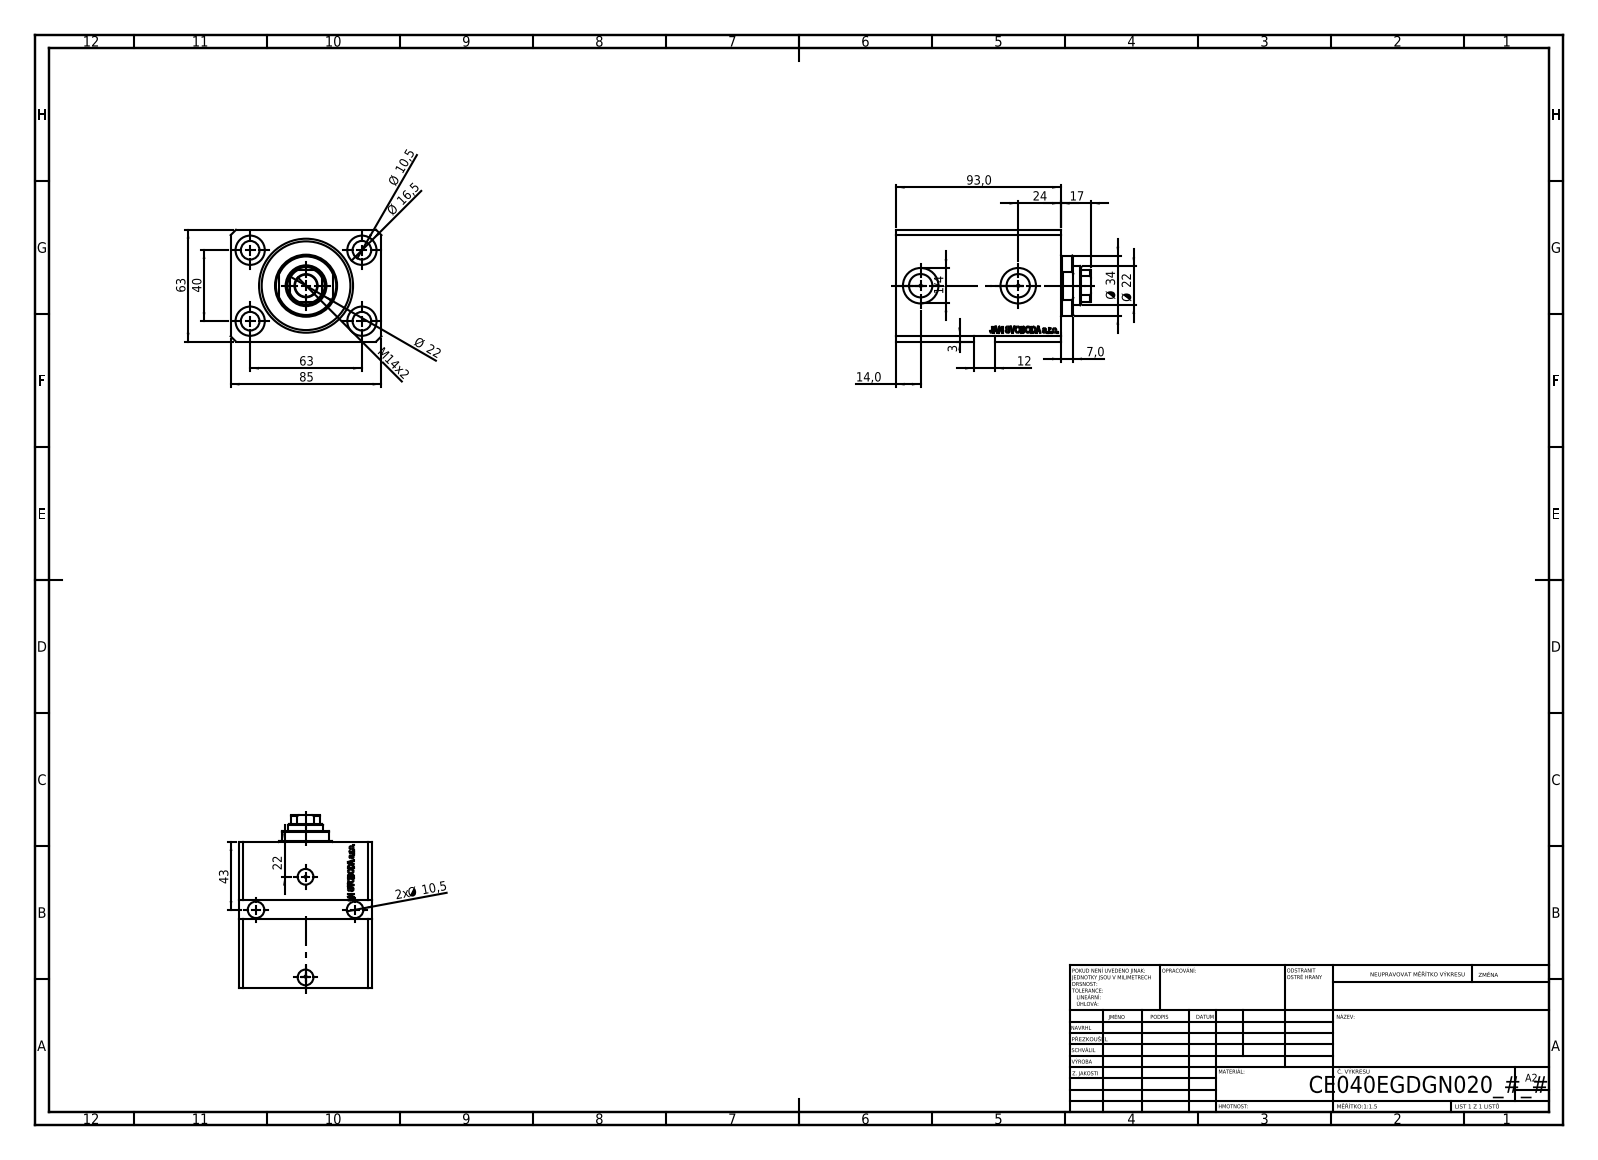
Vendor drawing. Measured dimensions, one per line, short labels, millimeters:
name: V250CE_VC_E; V250CE_C_VCP; V250CE_E_Body
written by: SolidWorks 2019 (CONFIG_CONTROL_DESIGN)
unit: mm
bodies: 3 solids, 933 faces (463 planar, 96 cylindrical, 374 other)
size: 110 × 85 × 63
volume: 423 550 mm³; area: 88 404 mm²
holes: 6× ⌀10.5, 4× ⌀1.25, 4× ⌀16.5, 2× ⌀10, 2× ⌀13.16, 2× ⌀20, 1× ⌀12.5, 1× ⌀22, 1× ⌀40, 1× ⌀53
bosses: 1× ⌀34
rounds: 1× R10.5
face distances: 63, 85, 93, 17, 76, 11.4, 64.6, 81.6, 56, 44.6
hole spacings: 37.31, 63, 37.86, 40, 52.88, 53.3, 74.63, 0.53
